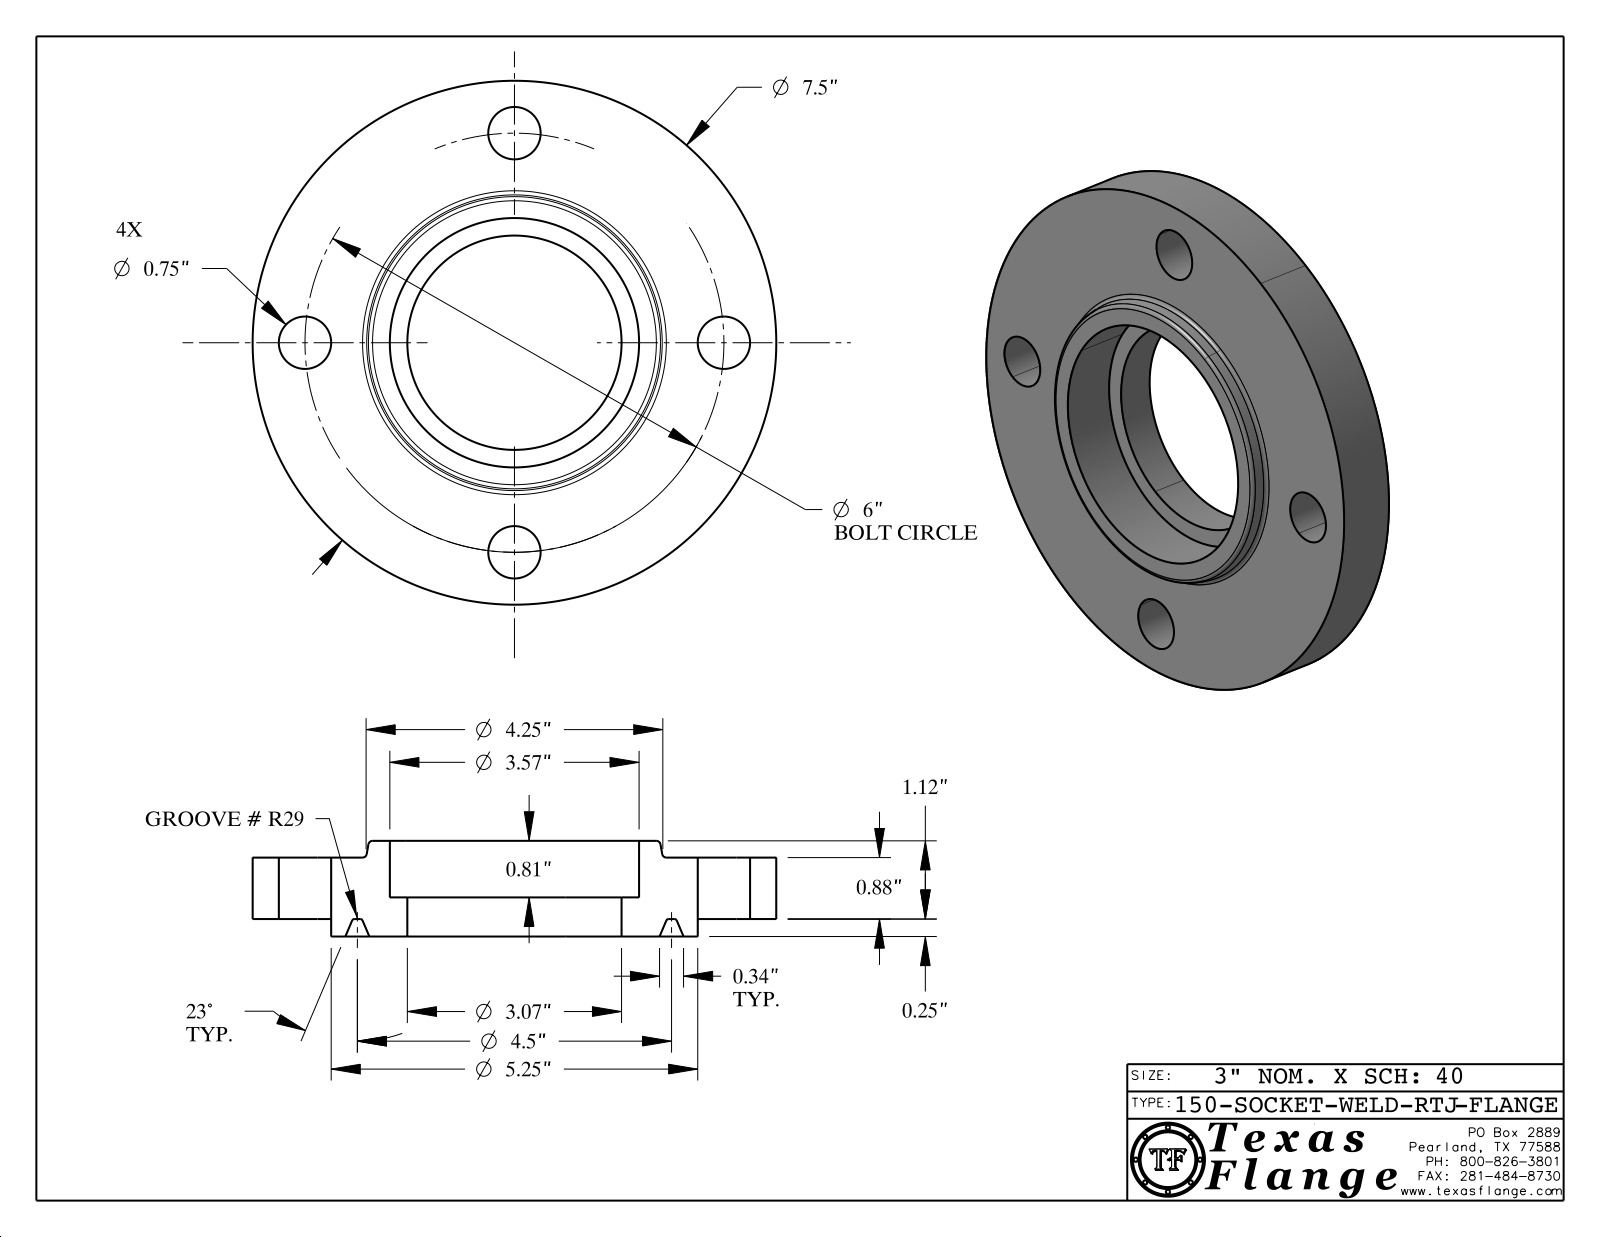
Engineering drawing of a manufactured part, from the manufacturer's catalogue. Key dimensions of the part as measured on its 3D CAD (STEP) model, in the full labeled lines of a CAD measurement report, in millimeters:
Part name (STEP PRODUCT): 150-SOCKET-WELD-RTJ
STEP written by: CATIA V5 STEP AP214 (AUTOMOTIVE_DESIGN)
Units: millimetres
Bodies: 1 solid, 422 faces (372 planar, 36 cylindrical, 14 other)
Overall size (bounding box): 190.5 × 190.5 × 34.8
Volume: 540 400 mm³ · Surface area: 80 320 mm²
Round holes (diameter × count): ⌀19.1 ×4, ⌀12.6 ×1, ⌀77.9 ×1, ⌀90.7 ×1
Round bosses / shafts (diameter × count): ⌀0.8 ×8, ⌀190.5 ×1, ⌀133.4 ×1, ⌀9.9 ×1
Main face-to-face distances: 22.4, 6.4, 28.7, 34.8, 28.4, 6.1, 14.2, 7.9, 14.5, 20.6
Hole centre spacings: 76.2, 107.8, 58.3, 140.8, 152.4
